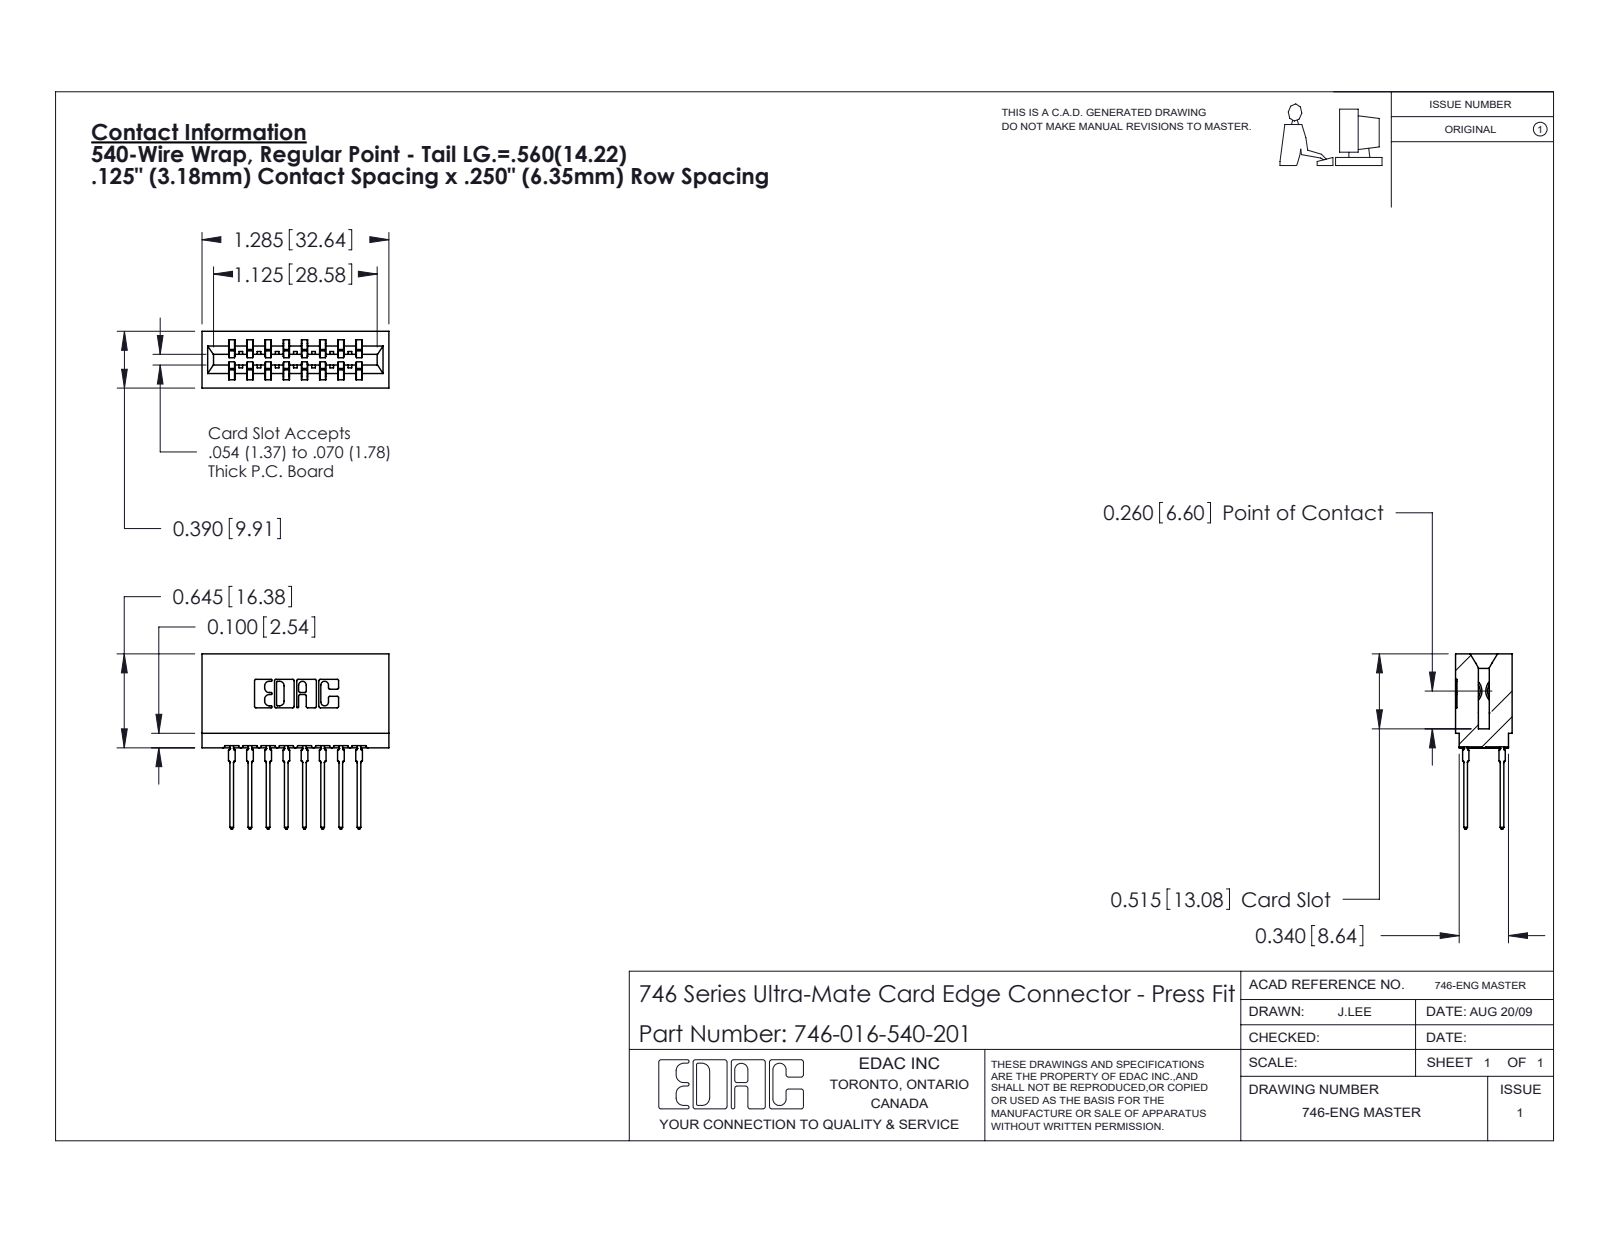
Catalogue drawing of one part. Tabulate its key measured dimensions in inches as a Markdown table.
| quantity | value |
| --- | --- |
| part name | 746-016-540-201; 746-292-001_540; 746 Part_.515 Slot Depth - 01 |
| STEP written by | SolidWorks 2020 (CONFIG_CONTROL_DESIGN) |
| units | inches |
| bodies | 17 solids, 1529 faces (791 planar, 322 cylindrical, 416 other) |
| overall size | 1.285 × 1.204 × 0.39 |
| volume | 0.23 in³ |
| surface area | 8.664 in² |
| partial cylindrical surfaces (radius × count) | 0.021 × 32, 0.01 × 22, 0.015 × 9, 0.005 × 8, 0.011 × 8, 0.007 × 6, 0.031 × 6, 0.026 × 3 |
| main face-to-face distances | 0.25, 0.333, 0.057, 0.042, 0.125, 0.5, 0.292, 0.208, 0.375, 0.125 |
